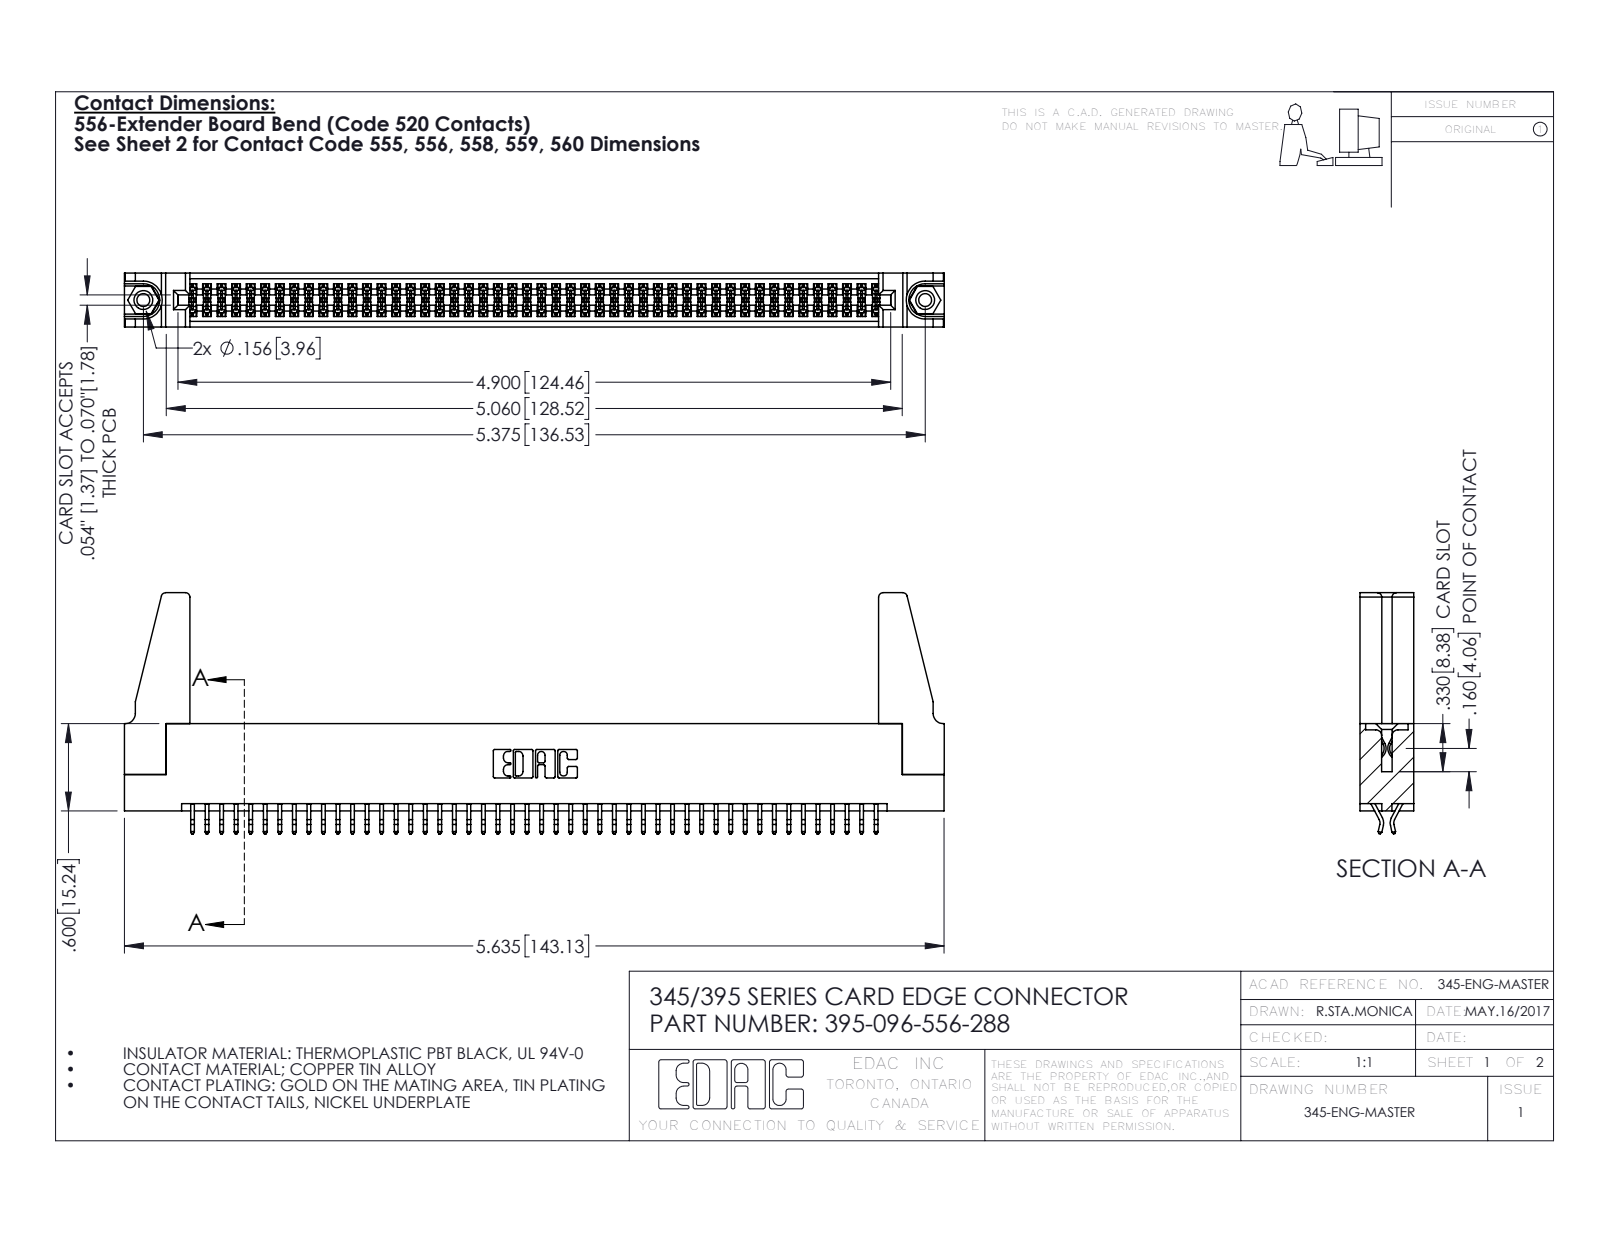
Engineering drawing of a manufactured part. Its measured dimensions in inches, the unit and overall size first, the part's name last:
Units: inches
Overall size (bounding box): 5.636 × 1.657 × 0.37
Round holes (diameter × count): ⌀0.089 ×2, ⌀0.125 ×2, ⌀0.156 ×2, ⌀0.064 ×1
Round bosses / shafts (diameter × count): ⌀0.155 ×2
Partial cylindrical surfaces — rounded edges, fillets, slot ends (radius × count): R0.006 ×144, R0.01 ×22, R0.03 ×8, R0.007 ×6, R0.031 ×6, R0.026 ×3, R0.01 ×2, R0.014 ×2
Main face-to-face distances: 0.072, 0.298, 0.37, 0.2, 0.025, 0.098, 0.272, 0.225, 0.175, 0.149
Hole centre spacings: 0.27, 5.139, 5.375
Volume: 1.05 in³ · Surface area: 36.87 in²
Bodies: 101 solids, 5626 faces (3704 planar, 1906 cylindrical, 16 other)
Part name (STEP PRODUCT): 345-250-001_345-250-001-102; 345 Part_Flush Mounting Lugs - 0.156 Dia-TH; 345-292-001_556 Tail; 395-096-556-288 (+1 more)
STEP written by: SolidWorks 2016 (CONFIG_CONTROL_DESIGN)
